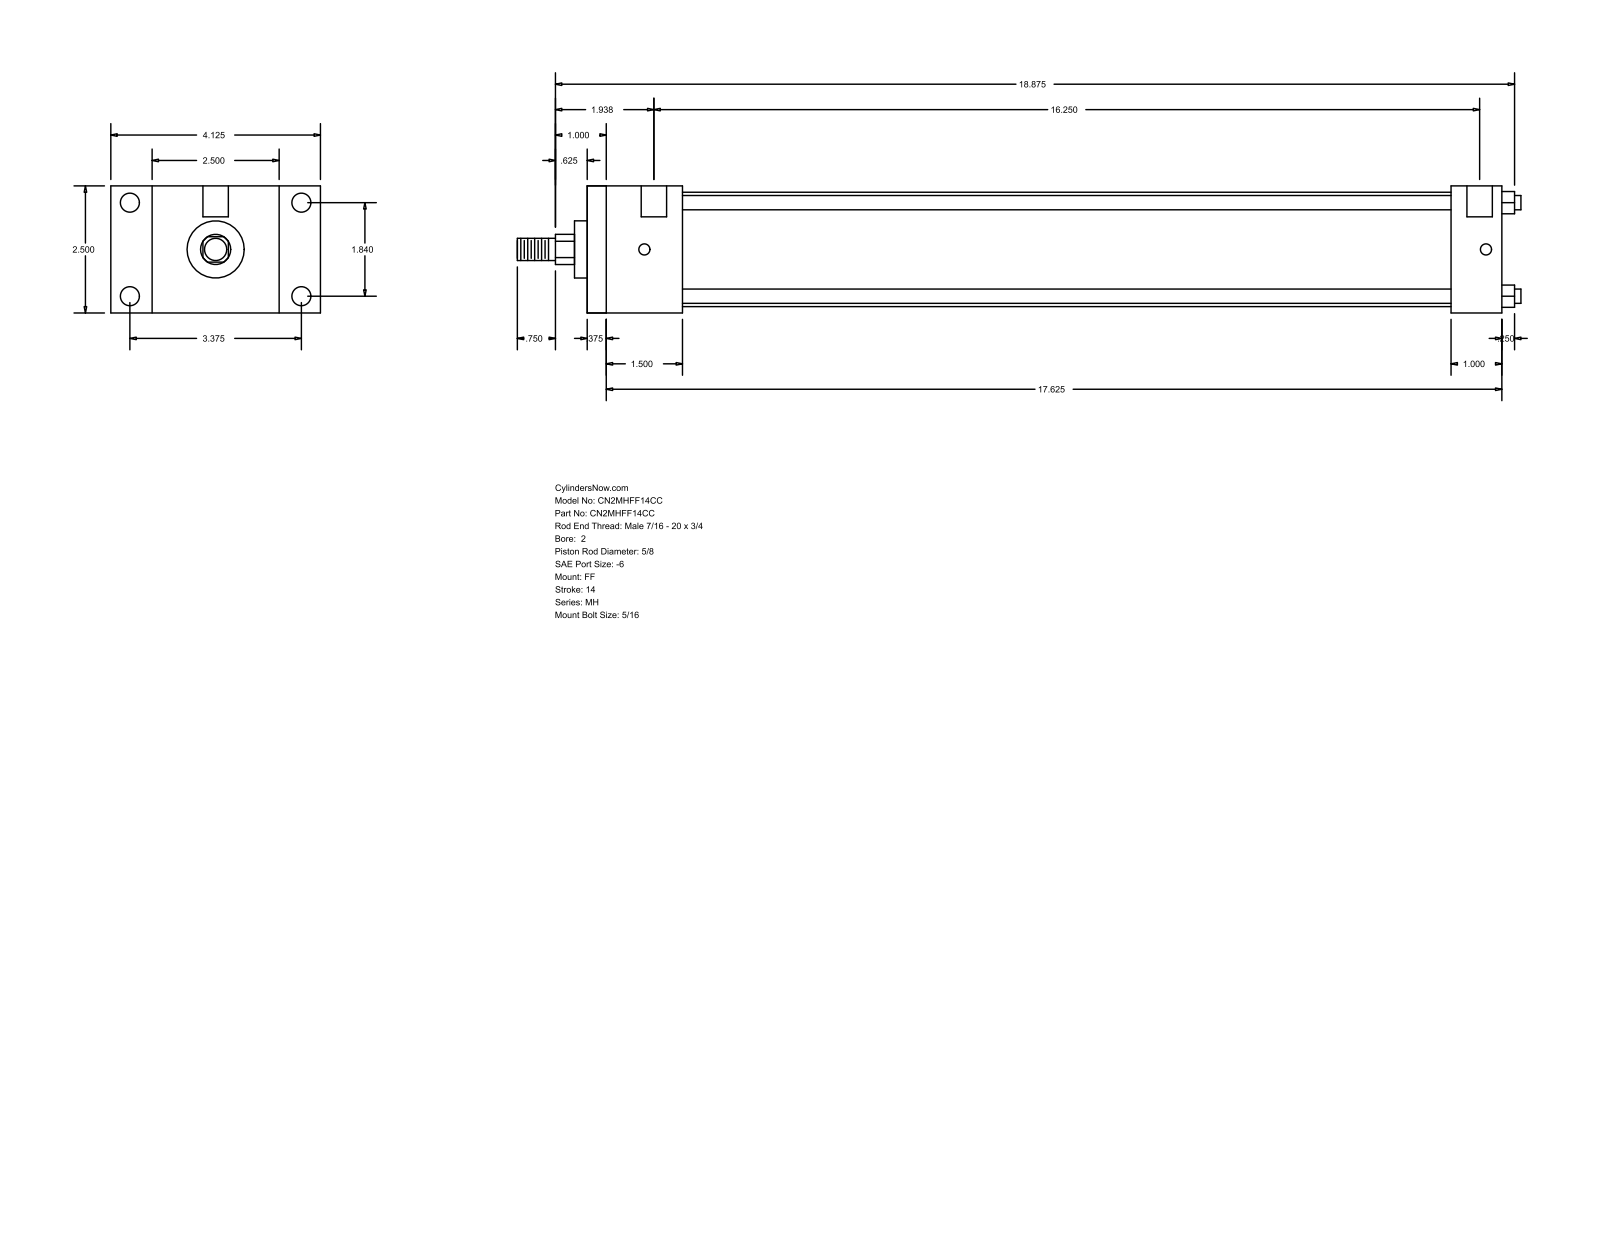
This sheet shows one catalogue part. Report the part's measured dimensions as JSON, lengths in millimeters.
{"part_name": "MH_FF__0200_0.625", "step_written_by": "GSSL Pune (CONFIG_CONTROL_DESIGN)", "units": "millimeters", "bodies": {"solids": 0, "faces": 92, "planar": 64, "cylindrical": 28, "other": 0}, "overall_size": [501.65, 104.78, 63.5], "round_holes": [[5.56, 4], [9.53, 4], [12.7, 2]], "round_bosses_or_shafts": [[7.14, 4], [57.15, 1], [28.57, 1], [15.88, 1], [11.11, 1]], "partial_cylinders_radius": [[7.54, 1]], "face_to_face_distances": [63.5, 457.19, 9.52, 447.67, 38.1, 47.62, 431.8, 422.28, 384.18, 409.57], "hole_center_spacings": [46.74, 85.72, 97.63, 420.69, 3.18, 4.76, 412.75, 415.93]}
